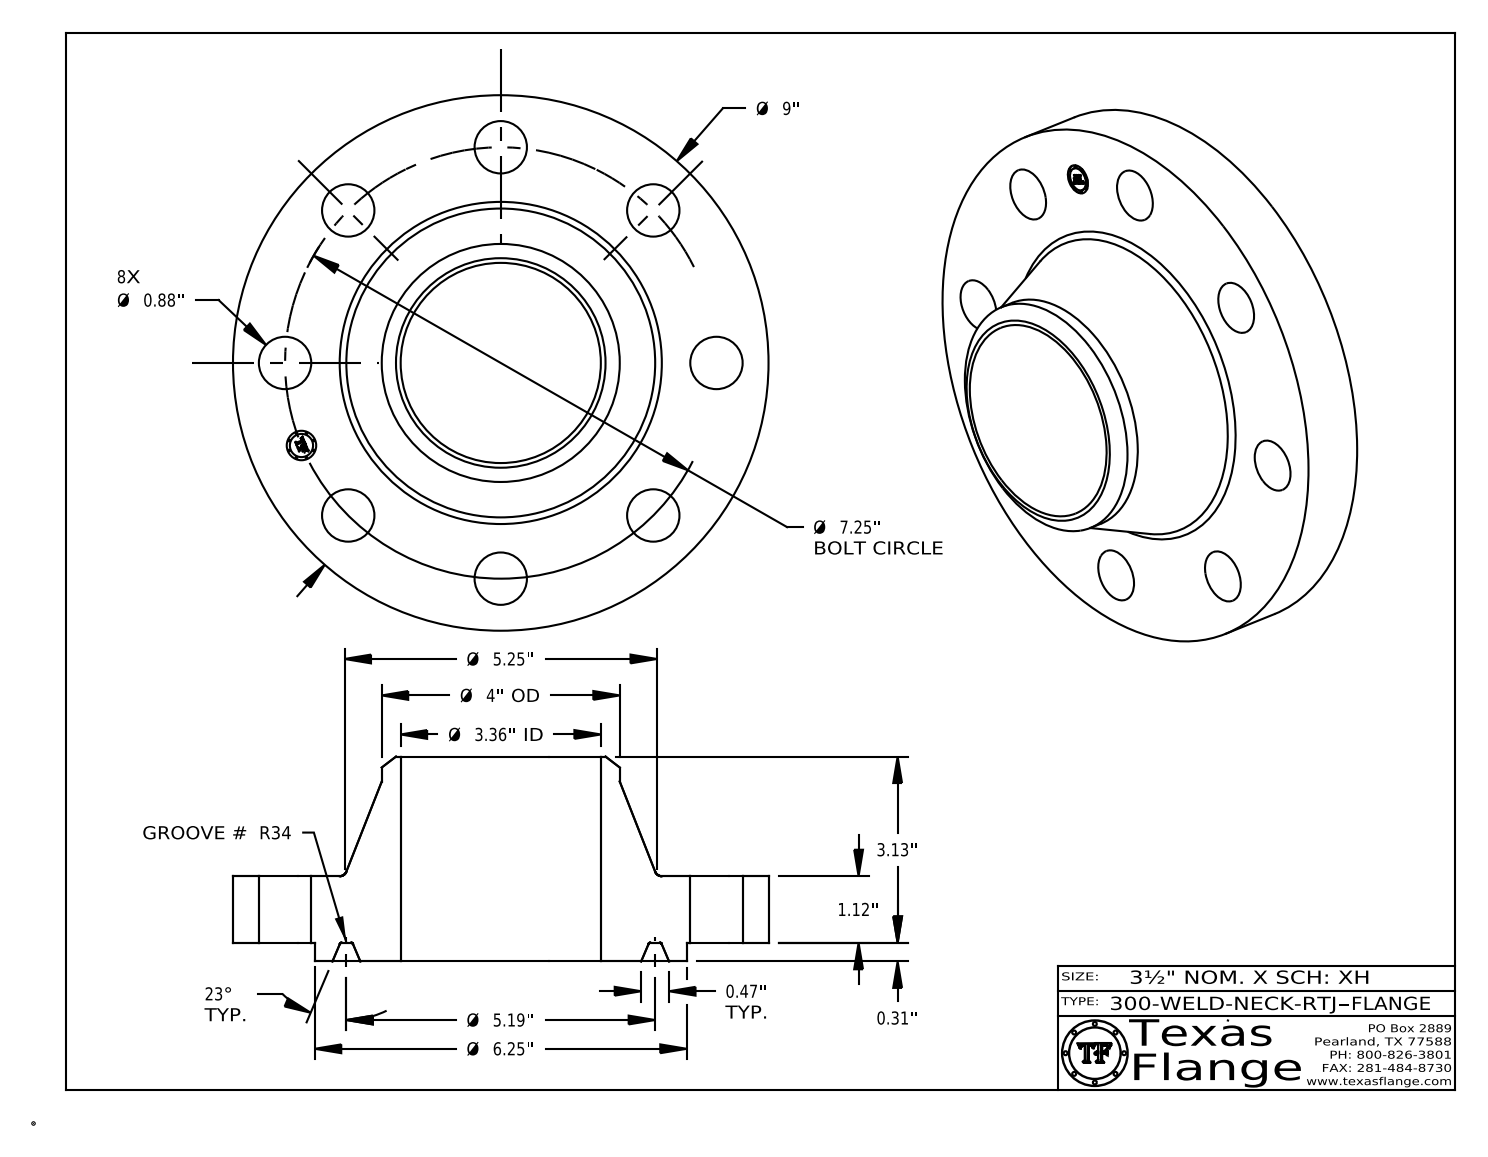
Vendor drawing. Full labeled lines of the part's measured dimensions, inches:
Part name (STEP PRODUCT): 300-WELD-NECK-RTJ
STEP written by: CATIA V5 STEP AP214 (AUTOMOTIVE_DESIGN)
Units: inches
Bodies: 1 solid, 429 faces (371 planar, 44 cylindrical, 14 other)
Overall size (bounding box): 9 × 9 × 3.443
Volume: 75 in³ · Surface area: 224.5 in²
Round holes (diameter × count): ⌀0.88 ×8, ⌀0.495 ×1, ⌀3.364 ×1
Round bosses / shafts (diameter × count): ⌀0.03 ×8, ⌀9 ×1, ⌀6.25 ×1, ⌀4 ×1, ⌀0.39 ×1
Main face-to-face distances: 1.12, 0.313, 1.433, 3.443, 3.13, 2.01, 1.418, 1.105, 0.015, 2.025
Hole centre spacings: 3.625, 2.774, 5.127, 6.698, 7.25, 1.415, 7.111, 4.028
